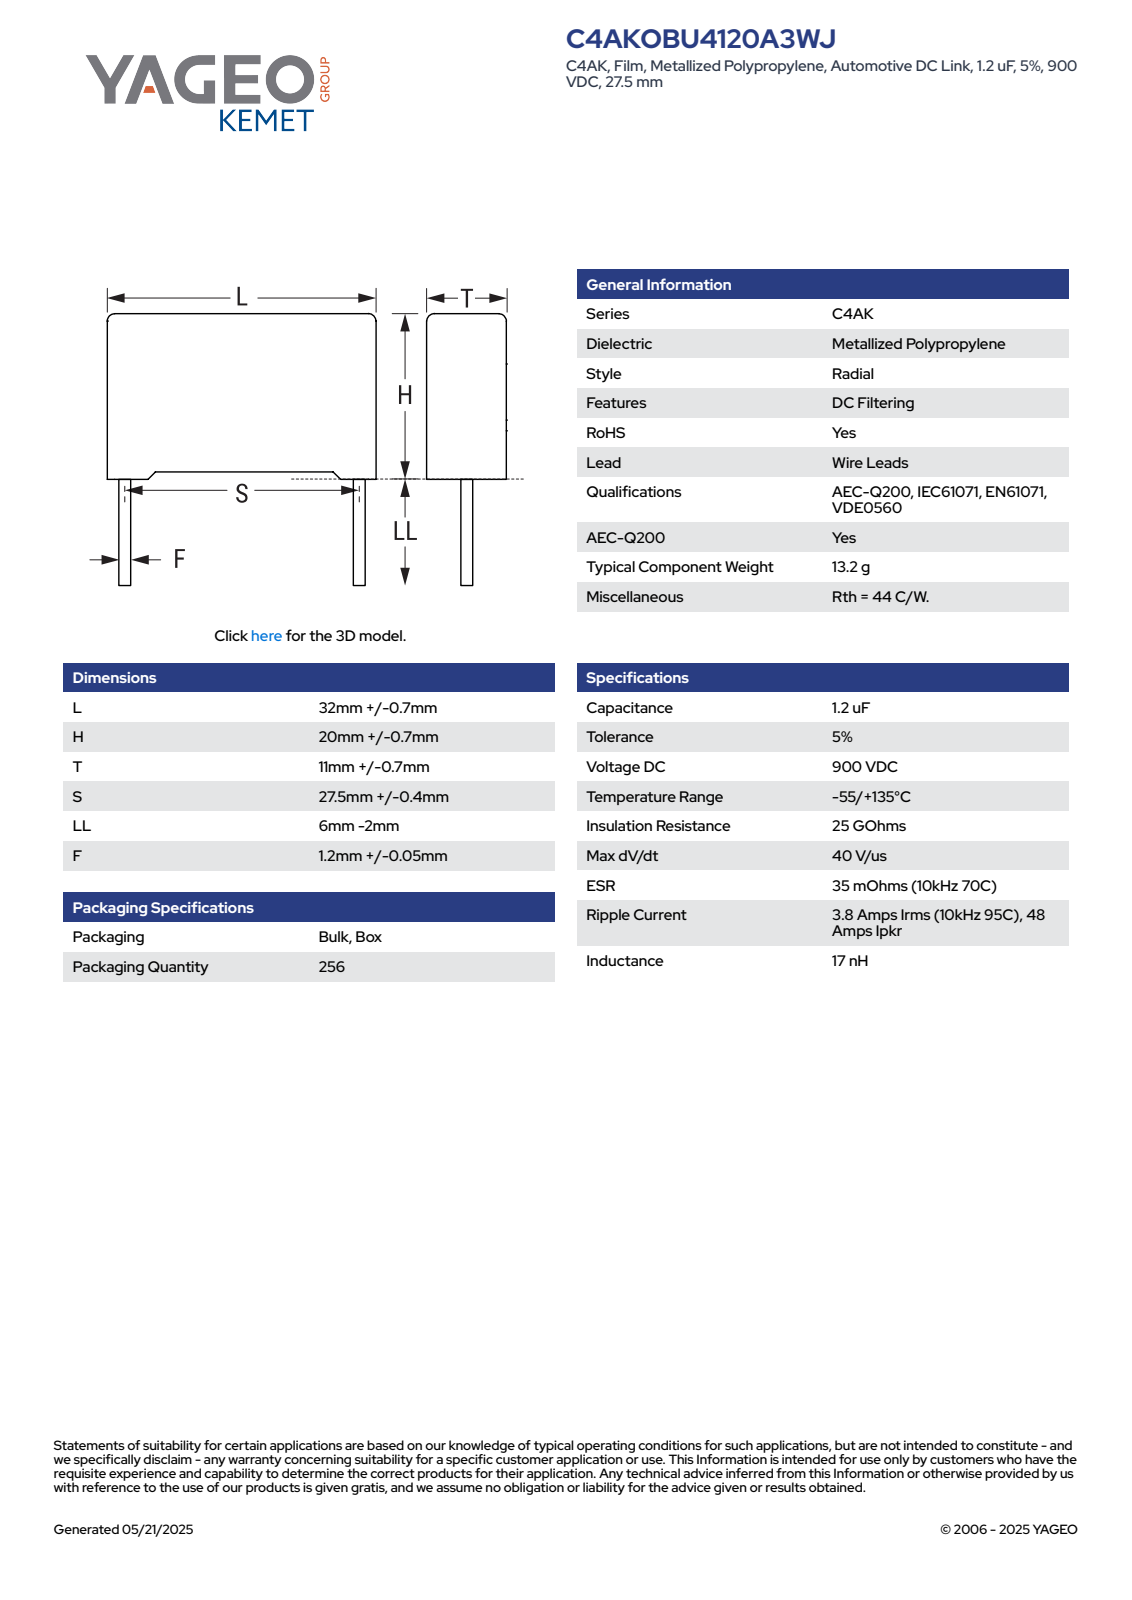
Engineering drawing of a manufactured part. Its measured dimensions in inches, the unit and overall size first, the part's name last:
Units: inches
Overall size (bounding box): 1.287 × 0.972 × 0.461
Round bosses / shafts (diameter × count): ⌀0.049 ×2
Partial cylindrical surfaces — rounded edges, fillets, slot ends (radius × count): R0.02 ×4
Main face-to-face distances: 0.461, 0.785, 1.287, 0.787, 0.028, 0.03, 0.815, 0.043, 1.244, 0.418
Volume: 0.468 in³ · Surface area: 4.177 in²
Bodies: 4 solids, 85 faces (77 planar, 8 cylindrical, 0 other)
Part name (STEP PRODUCT): CFR_RB2CFP_32X20X11_L32.7H20.7T11.7S27.5LL4F1.25
STEP written by: SolidWorks 2014 (AUTOMOTIVE_DESIGN)
